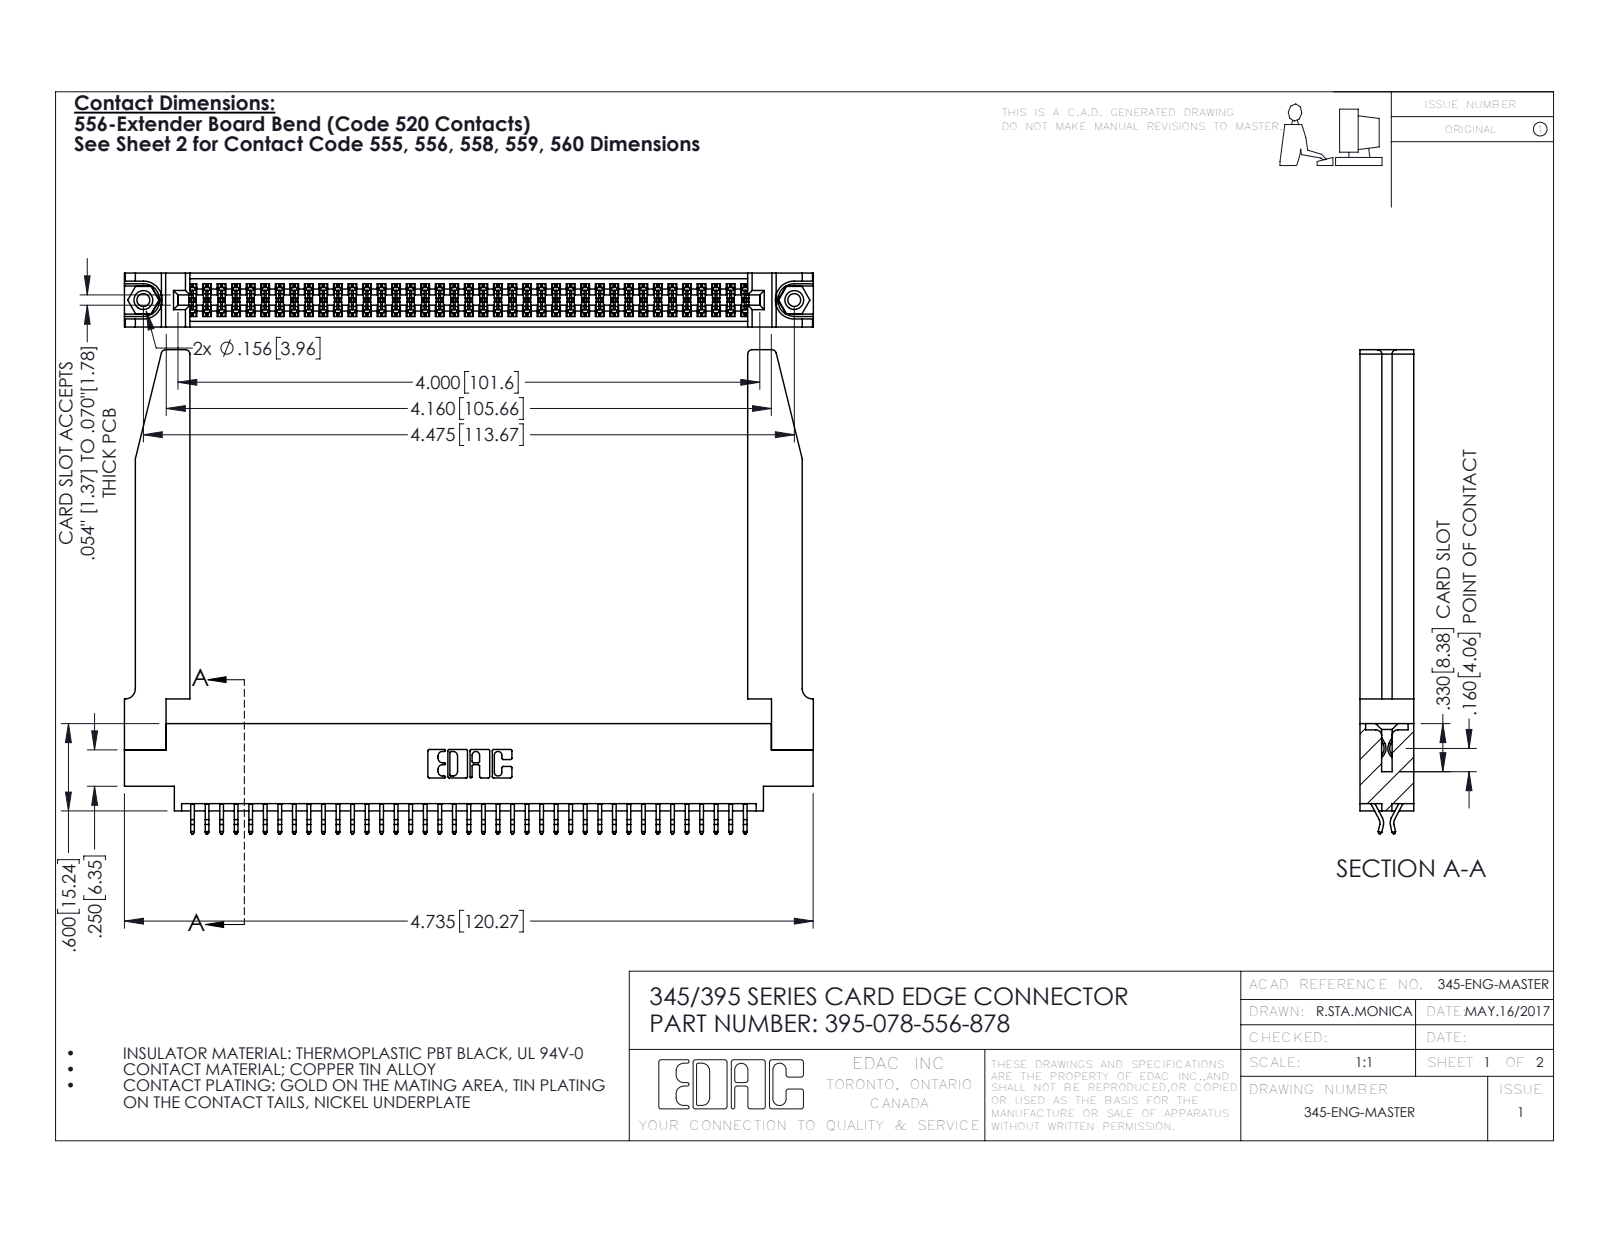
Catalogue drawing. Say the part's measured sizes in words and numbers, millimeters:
The part is named "345-292-001_556 Tail; 395-078-556-878; 345-220-078_345-220-078; 345-250-001_345-250-001-102 (+1 more)". Its 3-D file was written by "SolidWorks 2016 (CONFIG_CONTROL_DESIGN)". It is 83 solids with 4732 faces: 3112 planar, 1568 cylindrical and 52 other. Overall it measures 120.3 by 84.5 by 9.4 millimeters. Its volume is 19 300 cubic millimeters and its surface area 23 920 square millimeters. Round holes: 2 of diameter 2.3, 2 of diameter 3.2, 2 of diameter 4, 1 of diameter 1.6. Round bosses or shafts: 2 of diameter 3.9. Partial cylindrical surfaces (rounded edges, fillets, slot ends): 117 of radius 0.2, 22 of radius 0.3, 8 of radius 0.8, 6 of radius 0.2, 6 of radius 0.8, 3 of radius 0.7, 2 of radius 0.3, 2 of radius 0.4. The main face-to-face distances are 9.4, 1.8, 7.6, 0.6, 5.1, 2.5, 6.9, 5.7, 4.4, 3.8. The hole center spacings are 6.9, 107.7, 113.7.
